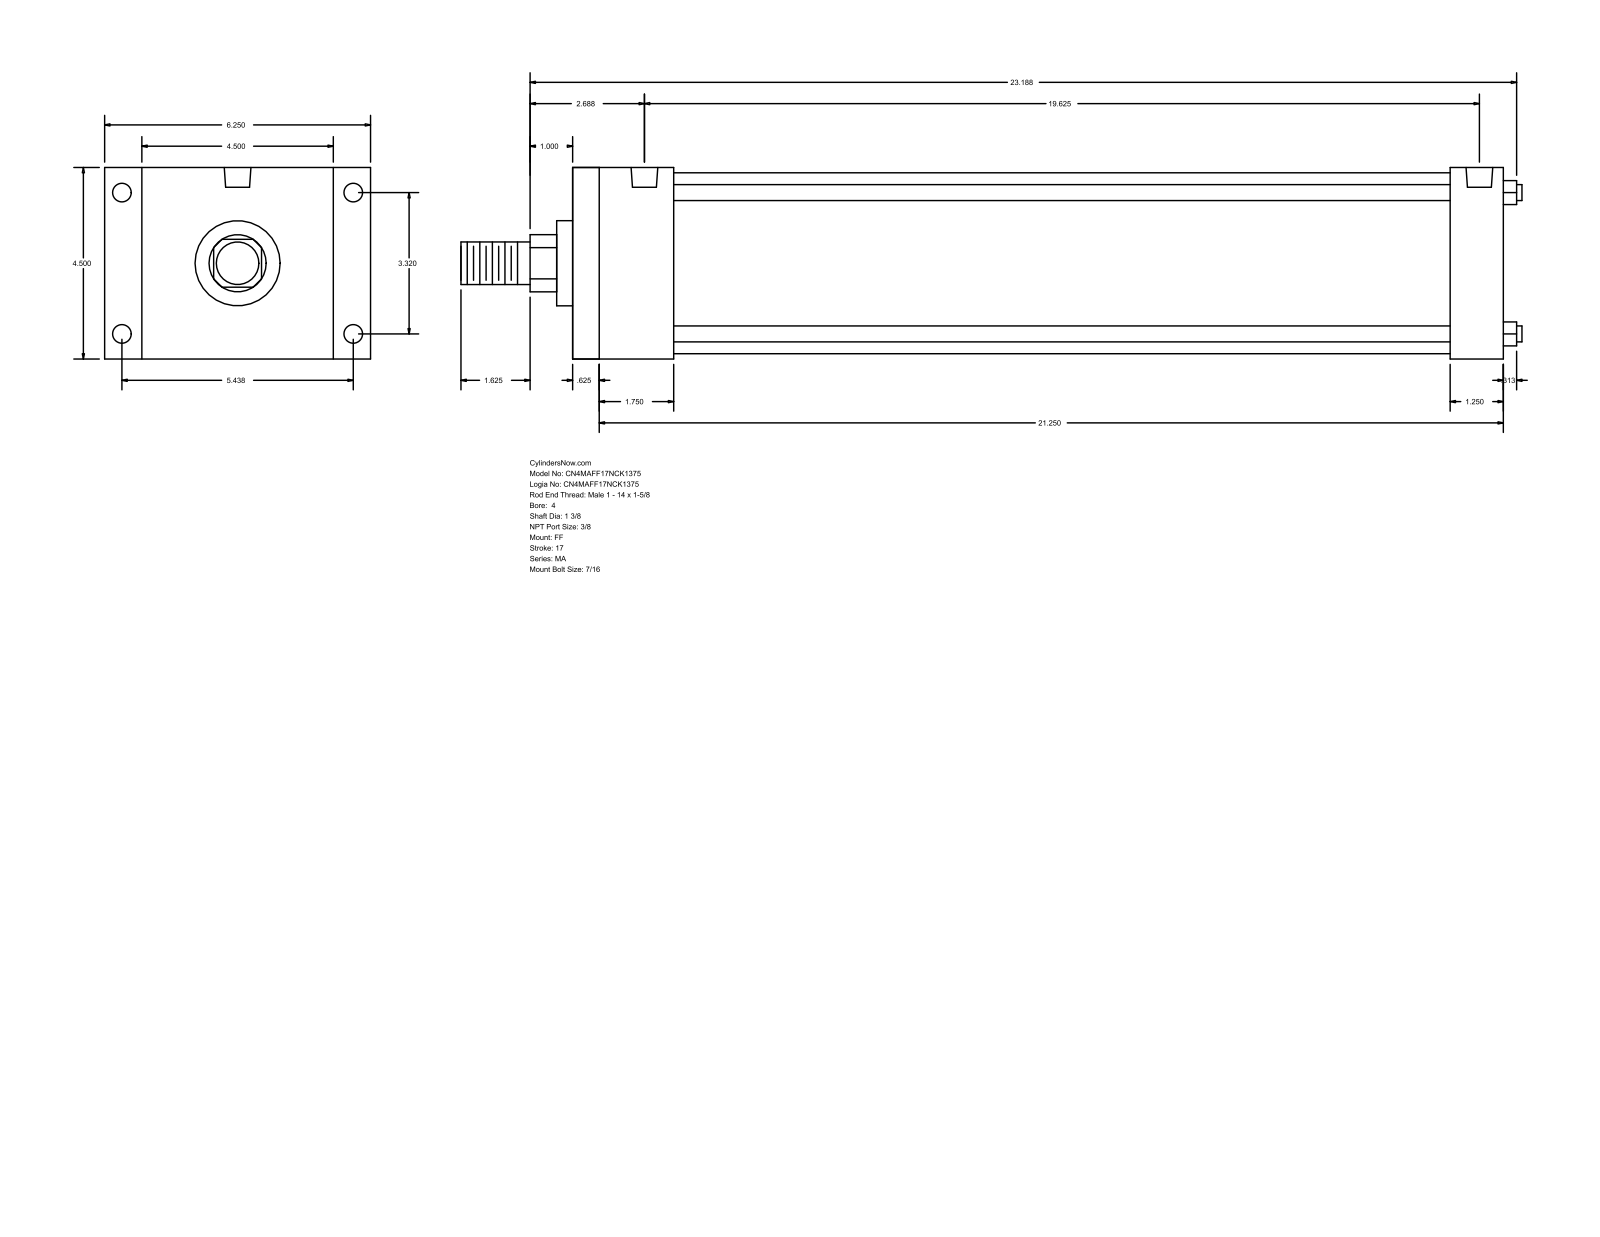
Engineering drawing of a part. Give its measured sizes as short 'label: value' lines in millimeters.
name: MA_FF__0400_1.375
written by: GSSL Pune (CONFIG_CONTROL_DESIGN)
unit: mm
bodies: 0 solids, 92 faces (64 planar, 28 cylindrical, 0 other)
size: 633.41 × 158.75 × 114.3
holes: 8× ⌀11.11, 2× ⌀15.93
bosses: 4× ⌀9.53, 1× ⌀107.95, 1× ⌀50.8, 1× ⌀34.92, 1× ⌀25.4
rounds: 1× R17.06
face distances: 114.3, 555.62, 15.87, 539.75, 22.23, 136.53, 523.87, 508, 31.75, 60.32
hole spacings: 84.32, 138.12, 161.82, 488.95, 4.76, 4.77, 493.71, 493.72
